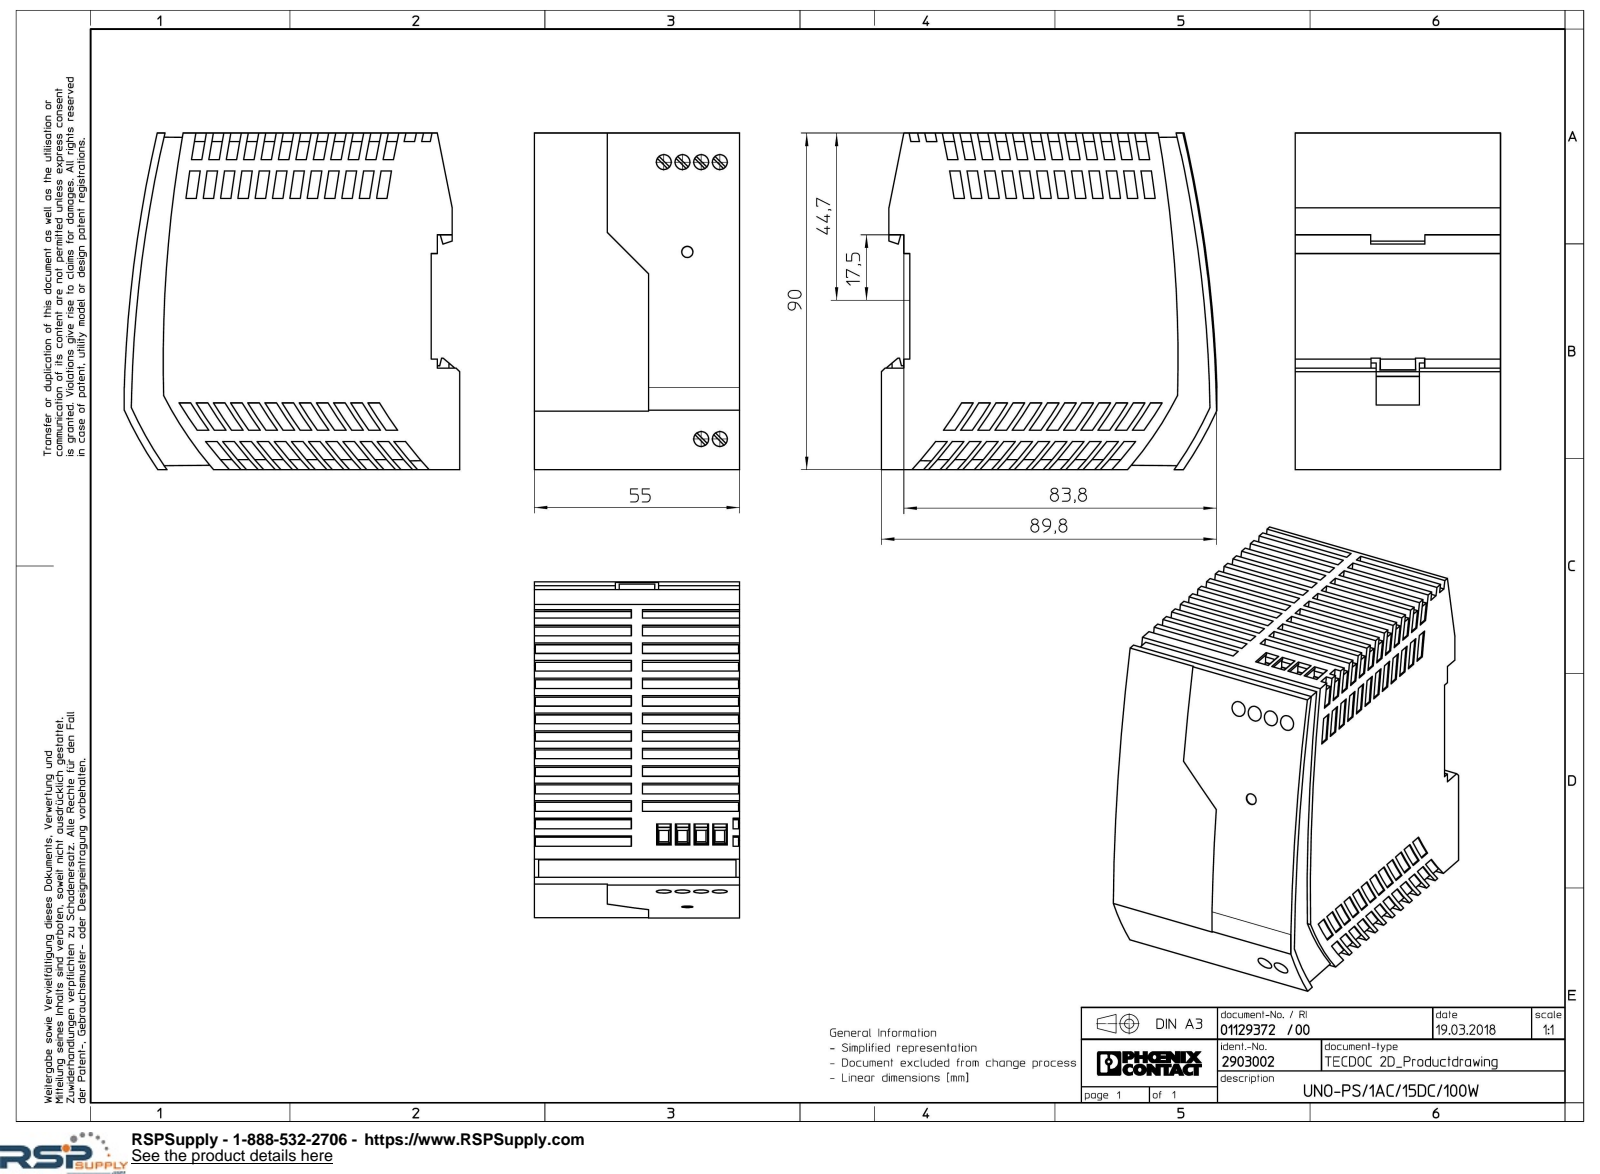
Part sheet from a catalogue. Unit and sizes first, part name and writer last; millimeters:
Units: millimetres
Overall size (bounding box): 90 × 89.87 × 55
Round holes (diameter × count): ⌀4 ×6
Partial cylindrical surfaces — rounded edges, fillets, slot ends (radius × count): R111 ×26, R98 ×1, R98.55 ×1, R100 ×1, R282.66 ×1, R284.9 ×1, R286.76 ×1, R291.36 ×1
Main face-to-face distances: 55, 2.3, 87.7, 90, 2.7, 85, 87.3, 54.7, 7.6, 54.4
Hole centre spacings: 5, 74.17, 10, 74, 74.67, 15, 75.5
Volume: 395 571 mm³ · Surface area: 43 992 mm²
Bodies: 1 solid, 779 faces (558 planar, 219 cylindrical, 2 other)
Part name (STEP PRODUCT): UNO_PS_1AC_15DC_100W-select
STEP written by: Creo Elements/Direct Modeling 18.1I 14-Aug-2016 (C) Parametric Technology GmbH (AUTOMOTIVE_DESIGN)
